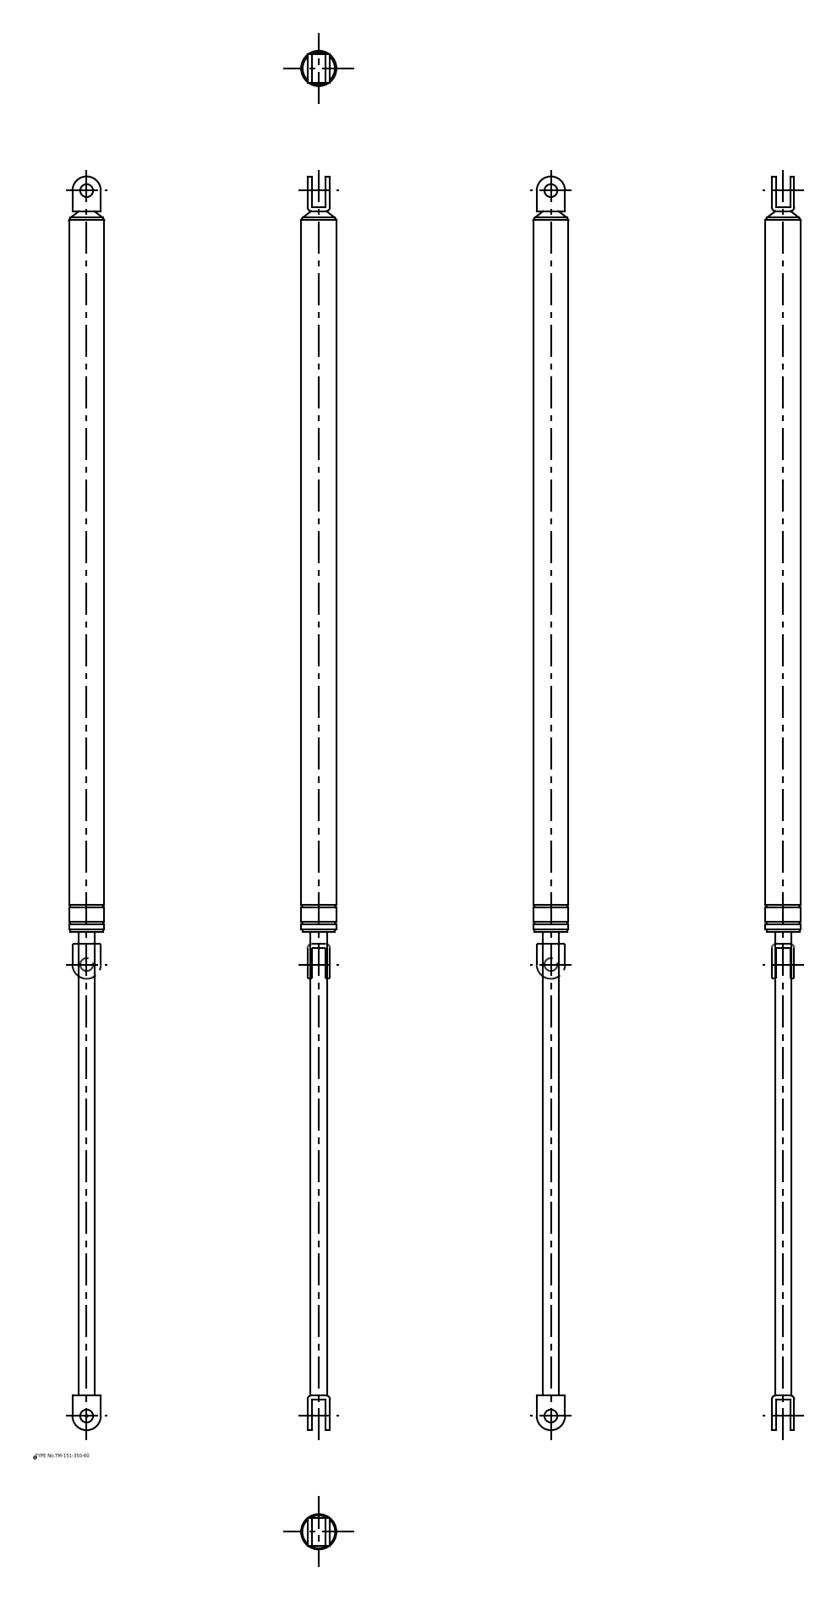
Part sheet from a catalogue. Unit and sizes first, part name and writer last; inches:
Units: inches
Overall size (bounding box): 38.268 × 1.11 × 1.11
Round holes (diameter × count): ⌀0.394 ×2
Round bosses / shafts (diameter × count): ⌀1.11 ×1, ⌀1.079 ×1, ⌀1.004 ×1, ⌀0.492 ×1
Partial cylindrical surfaces — rounded edges, fillets, slot ends (radius × count): R0.126 ×4, R0.433 ×2
Main face-to-face distances: 0.126, 0.559, 0.685, 0.433, 0.866, 36.268, 14.26, 36.394, 22.134, 22.008
Hole centre spacings: 37.402
Volume: 23.15 in³ · Surface area: 106.9 in²
Bodies: 2 solids, 64 faces (22 planar, 32 cylindrical, 10 other)
Part name (STEP PRODUCT): TM_151_350_60; TM_151_350_60_div
STEP written by: spGate 16.7.1 (AUTOMOTIVE_DESIGN)
